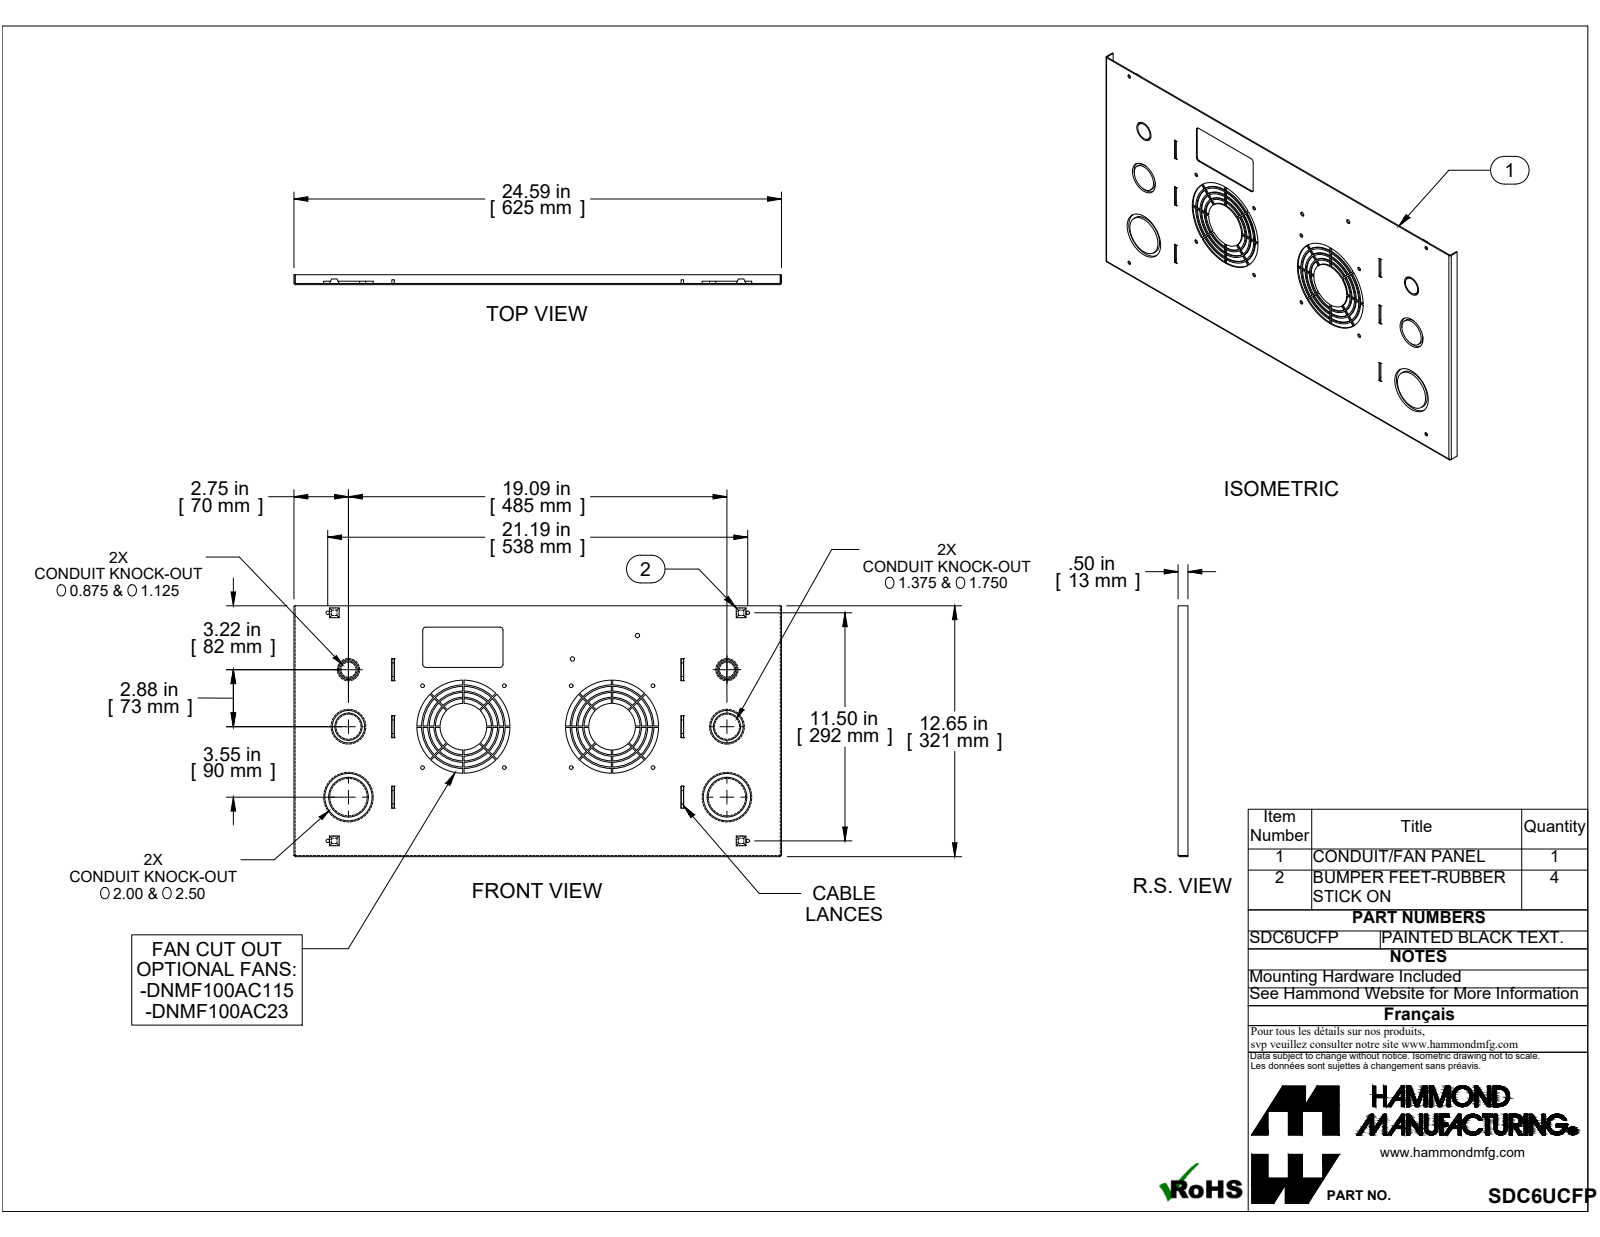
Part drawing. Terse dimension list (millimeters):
name: SDC6UCFP
written by: SolidWorks 2019 (CONFIG_CONTROL_DESIGN)
unit: mm
bodies: 5 solids, 532 faces (328 planar, 200 cylindrical, 4 other)
size: 624.7 × 321.3 × 12.7
volume: 292 000 mm³; area: 414 000 mm²
holes: 8× ⌀4.8, 4× ⌀4.5, 2× ⌀5.5, 2× ⌀19.3, 2× ⌀25.7, 2× ⌀32, 2× ⌀41.6, 2× ⌀47.9, 2× ⌀60.6, 2× ⌀71.8, 2× ⌀87.6, 2× ⌀103.4
bosses: 2× ⌀107, 2× ⌀91.3, 2× ⌀75.5, 2× ⌀63.5, 2× ⌀59.7, 2× ⌀50.8, 2× ⌀44.5, 2× ⌀34.9
rounds: 12× R1.4, 4× R4, 3× R0.7, 3× R2.2
face distances: 1.4, 3, 1.4, 623.2, 4.4, 621.8, 624.7, 1.5, 12.7, 11.3
hole spacings: 190.5, 74.1, 74.1, 104.8, 104.8, 147.7, 148.2, 206.4
